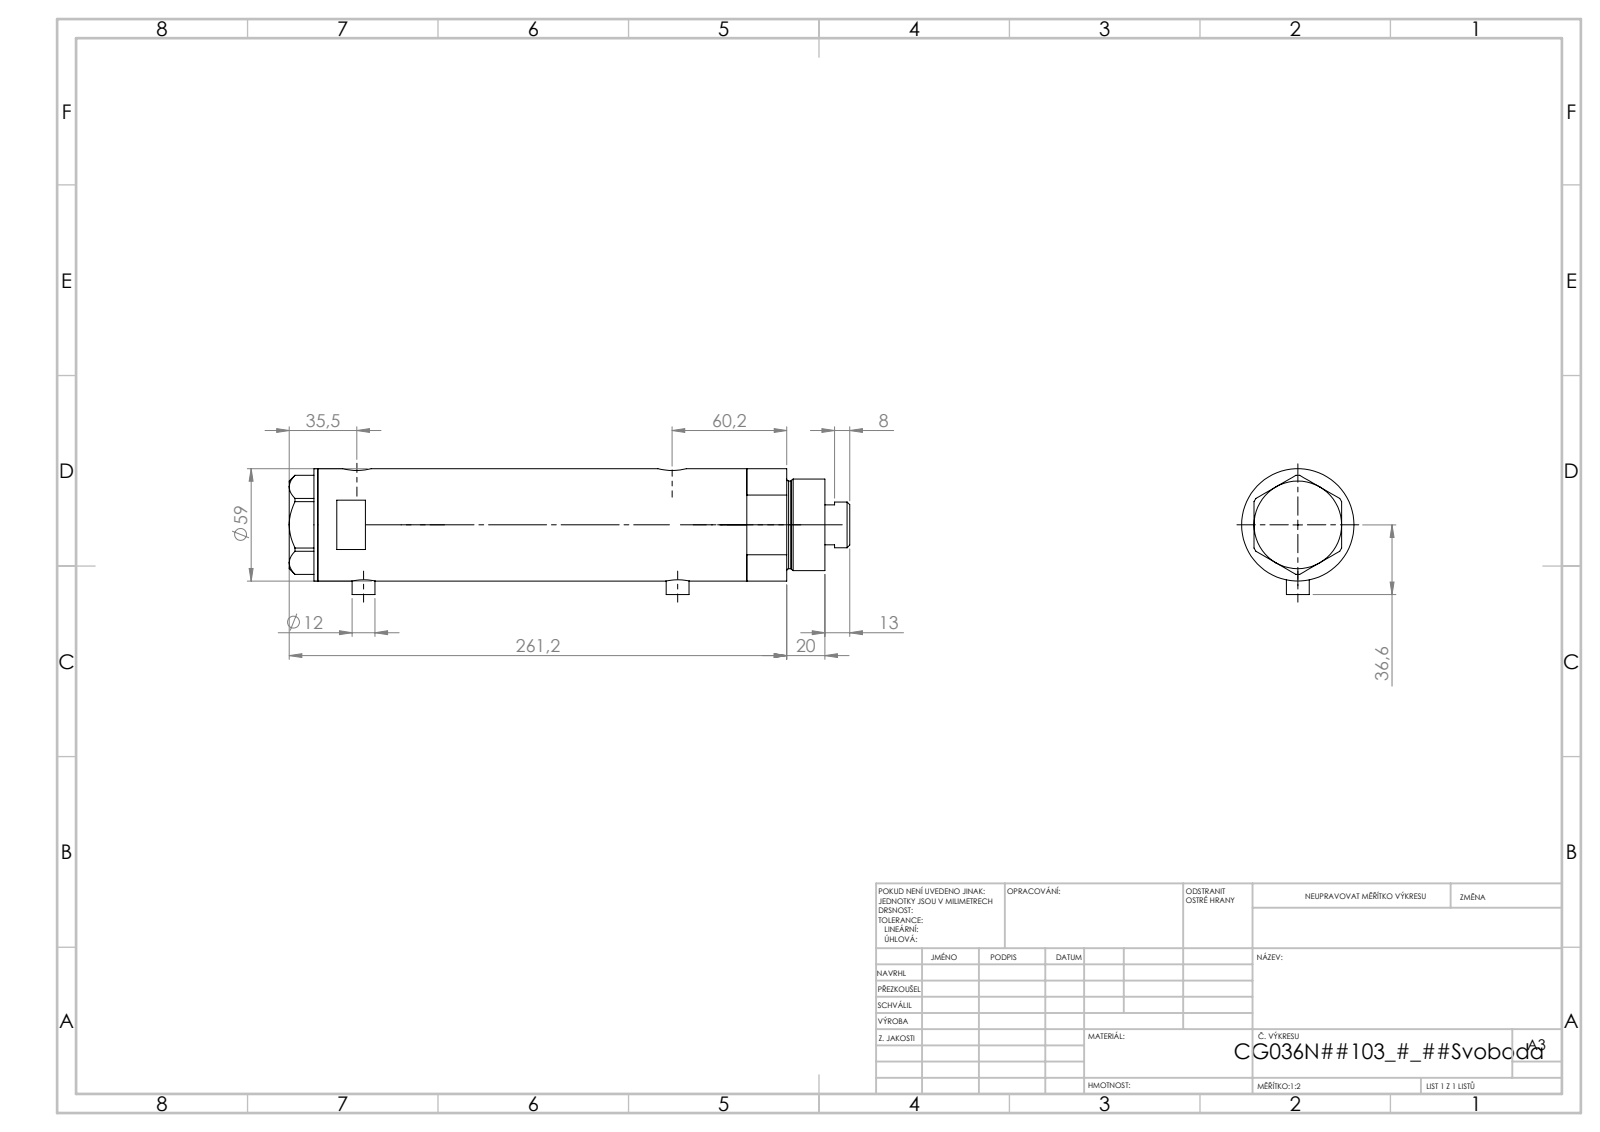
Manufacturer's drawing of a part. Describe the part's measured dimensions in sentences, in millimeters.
The part is named "V270CG_VC; V270CG_FRONT; V270CG_MIDDLE; V270CG_BACK". Its 3-D file was written by "SolidWorks 2019 (CONFIG_CONTROL_DESIGN)". It is 4 solids with 126 faces: 53 planar, 53 cylindrical and 20 other. Overall it measures 294.3 by 66.1 by 59 millimeters. Its volume is 680 390 cubic millimeters and its surface area 133 273 square millimeters. Round holes: 2 of diameter 5, 2 of diameter 9.73, 2 of diameter 12.5, 2 of diameter 15, 1 of diameter 8.5, 1 of diameter 25, 1 of diameter 26.5, 1 of diameter 36, 1 of diameter 40, 1 of diameter 52. Round bosses or shafts: 2 of diameter 12, 1 of diameter 59, 1 of diameter 48, 1 of diameter 46, 1 of diameter 24. The main face-to-face distances are 187.2, 23.5, 163.7, 15, 38.5, 202.2, 2, 266.2, 281.2, 242.7. The hole center spacings are 2.9, 3.5, 162, 164.9, 165.5, 168.4.
